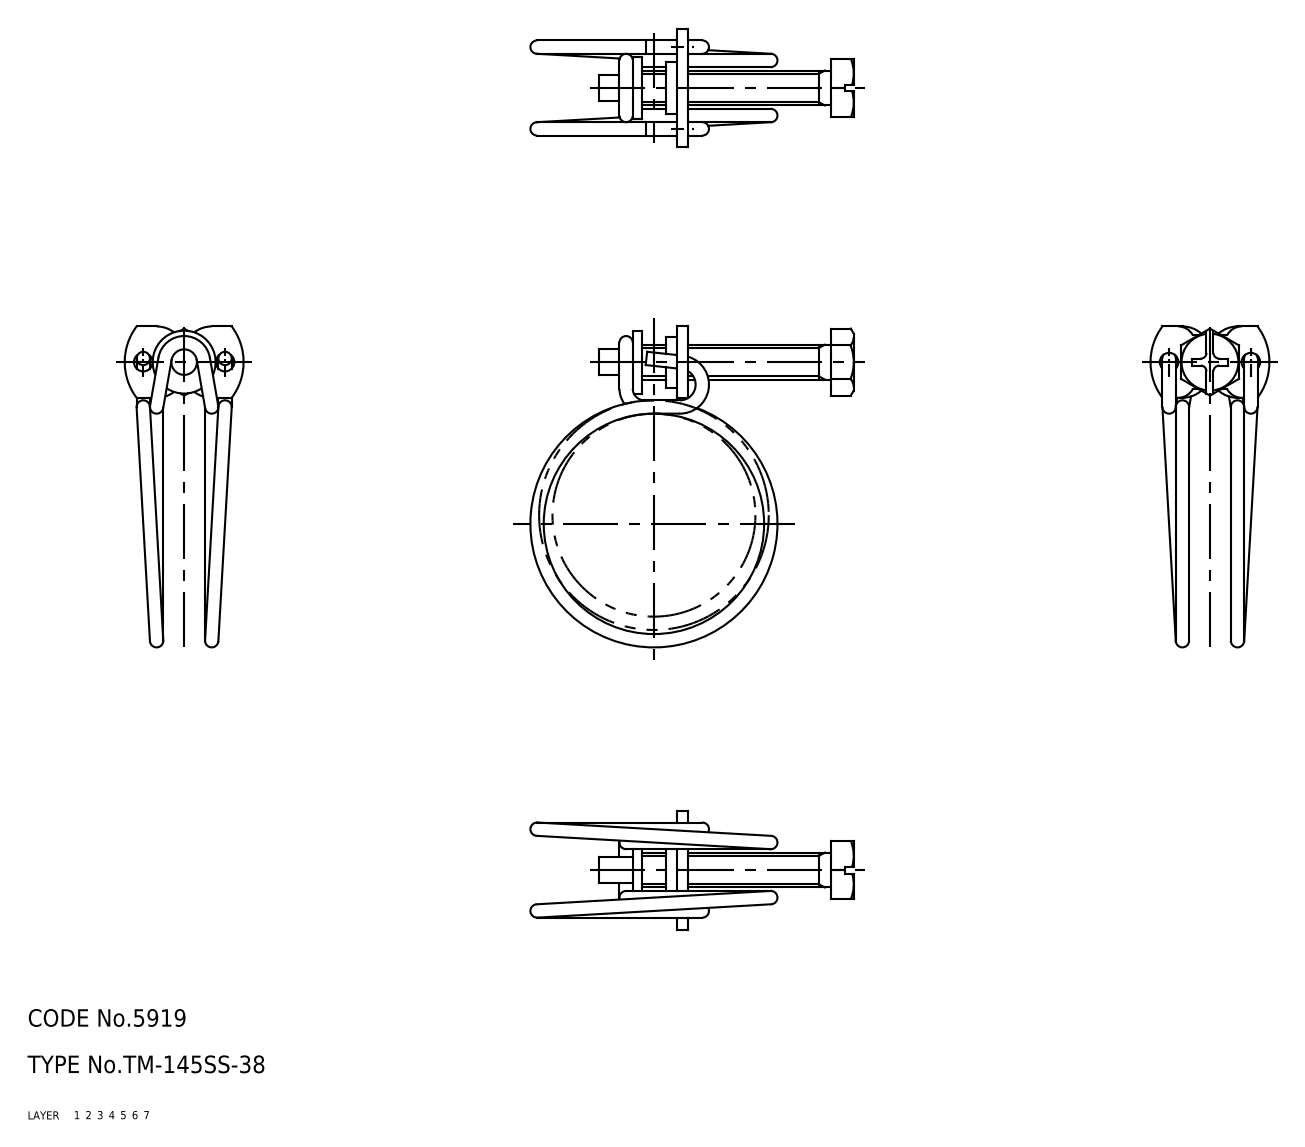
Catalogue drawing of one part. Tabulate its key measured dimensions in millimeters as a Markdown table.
| quantity | value |
| --- | --- |
| part name | 67116430; 67116443; 67116456 |
| STEP written by | CADfix (AUTOMOTIVE_DESIGN) |
| units | millimeters |
| bodies | 3 solids, 98 faces (0 planar, 0 cylindrical, 98 other) |
| overall size | 55.76 × 55.34 × 20.5 |
| volume | 3 268 mm³ |
| surface area | 4 275 mm² |
